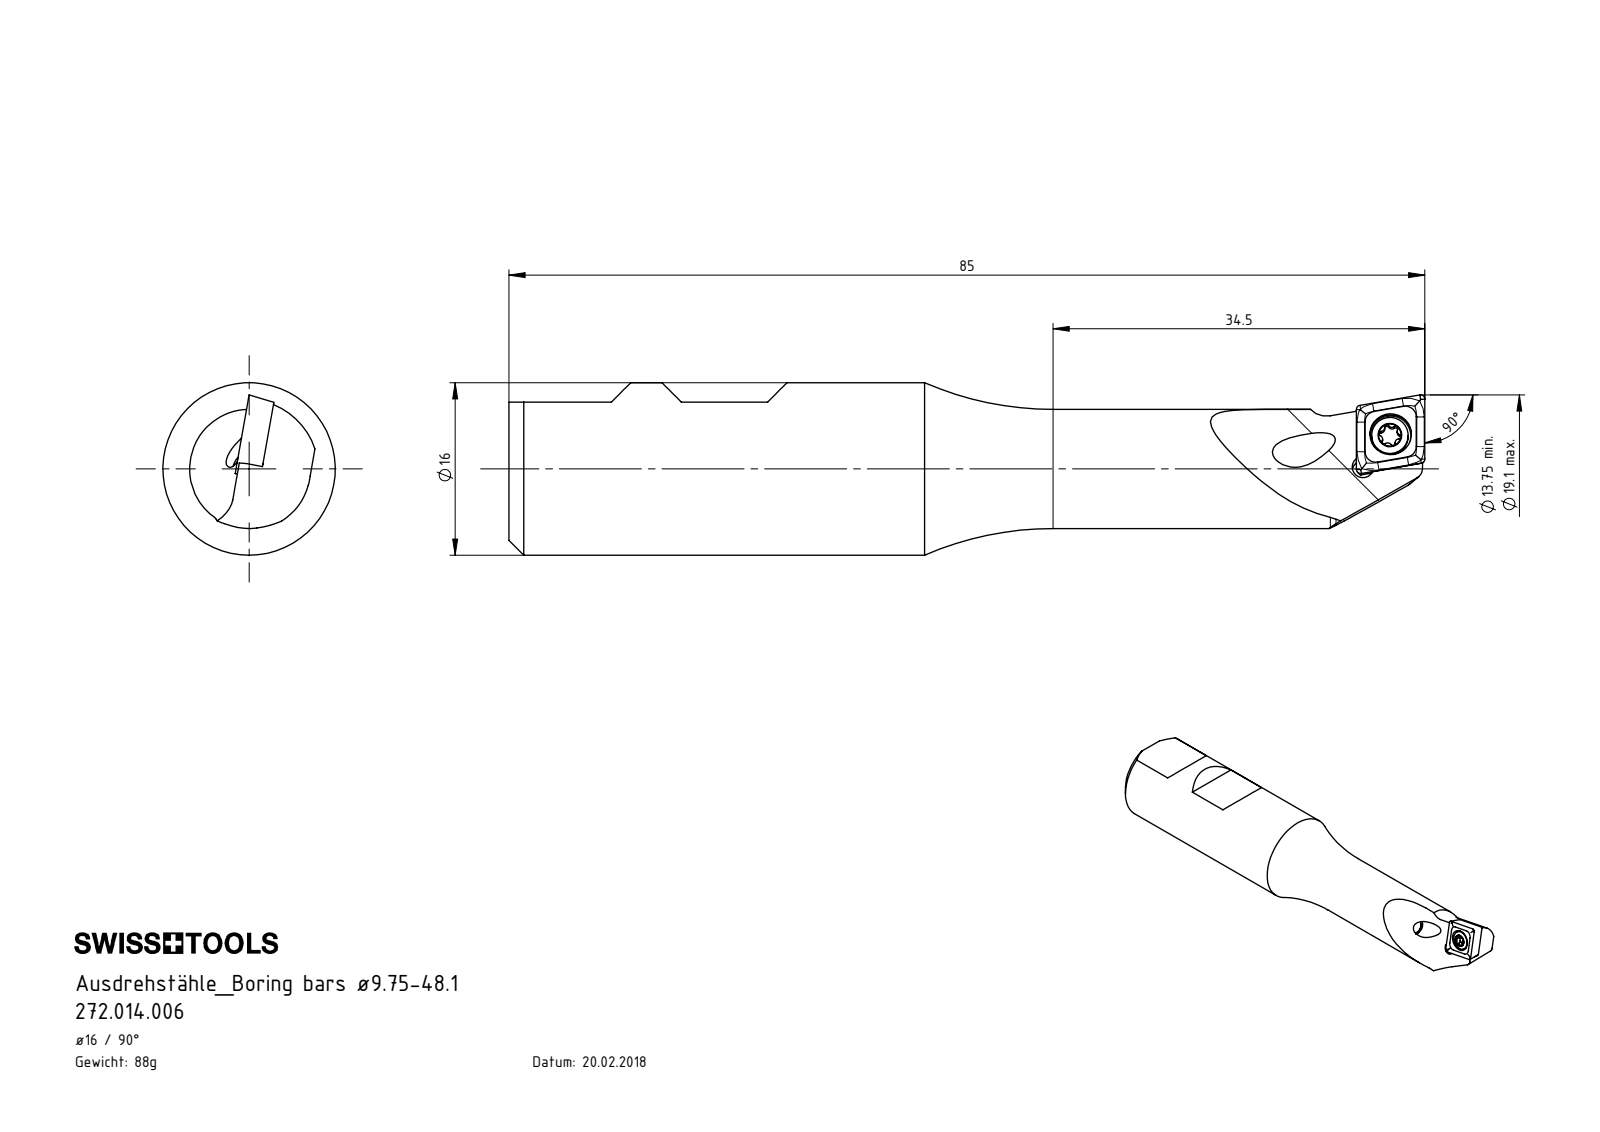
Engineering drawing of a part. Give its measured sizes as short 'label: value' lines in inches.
name: 272.014.006; WCA-ER2.001.006_A; CCMT060204; B14-WCA.K11.085_A
written by: SolidWorks 2017 (CONFIG_CONTROL_DESIGN)
unit: in
bodies: 3 solids, 130 faces (33 planar, 41 cylindrical, 56 other)
size: 3.346 × 0.63 × 0.63
volume: 0.68 in³; area: 7.198 in²
holes: 2× ⌀0.118, 1× ⌀0.079, 1× ⌀0.081, 1× ⌀0.11, 1× ⌀0.152
bosses: 1× ⌀0.63, 1× ⌀0.435, 1× ⌀0.134, 1× ⌀0.098
rounds: 6× R0.008, 5× R0.014, 1× R0.014, 1× R0.039, 1× R0.224, 1× R0.256, 1× R0.315
face distances: 0.085, 0.086, 0.404, 0.178, 0.178, 0.263, 0.272, 0.094, 0.094, 3.101
hole spacings: 0.153, 0.157
